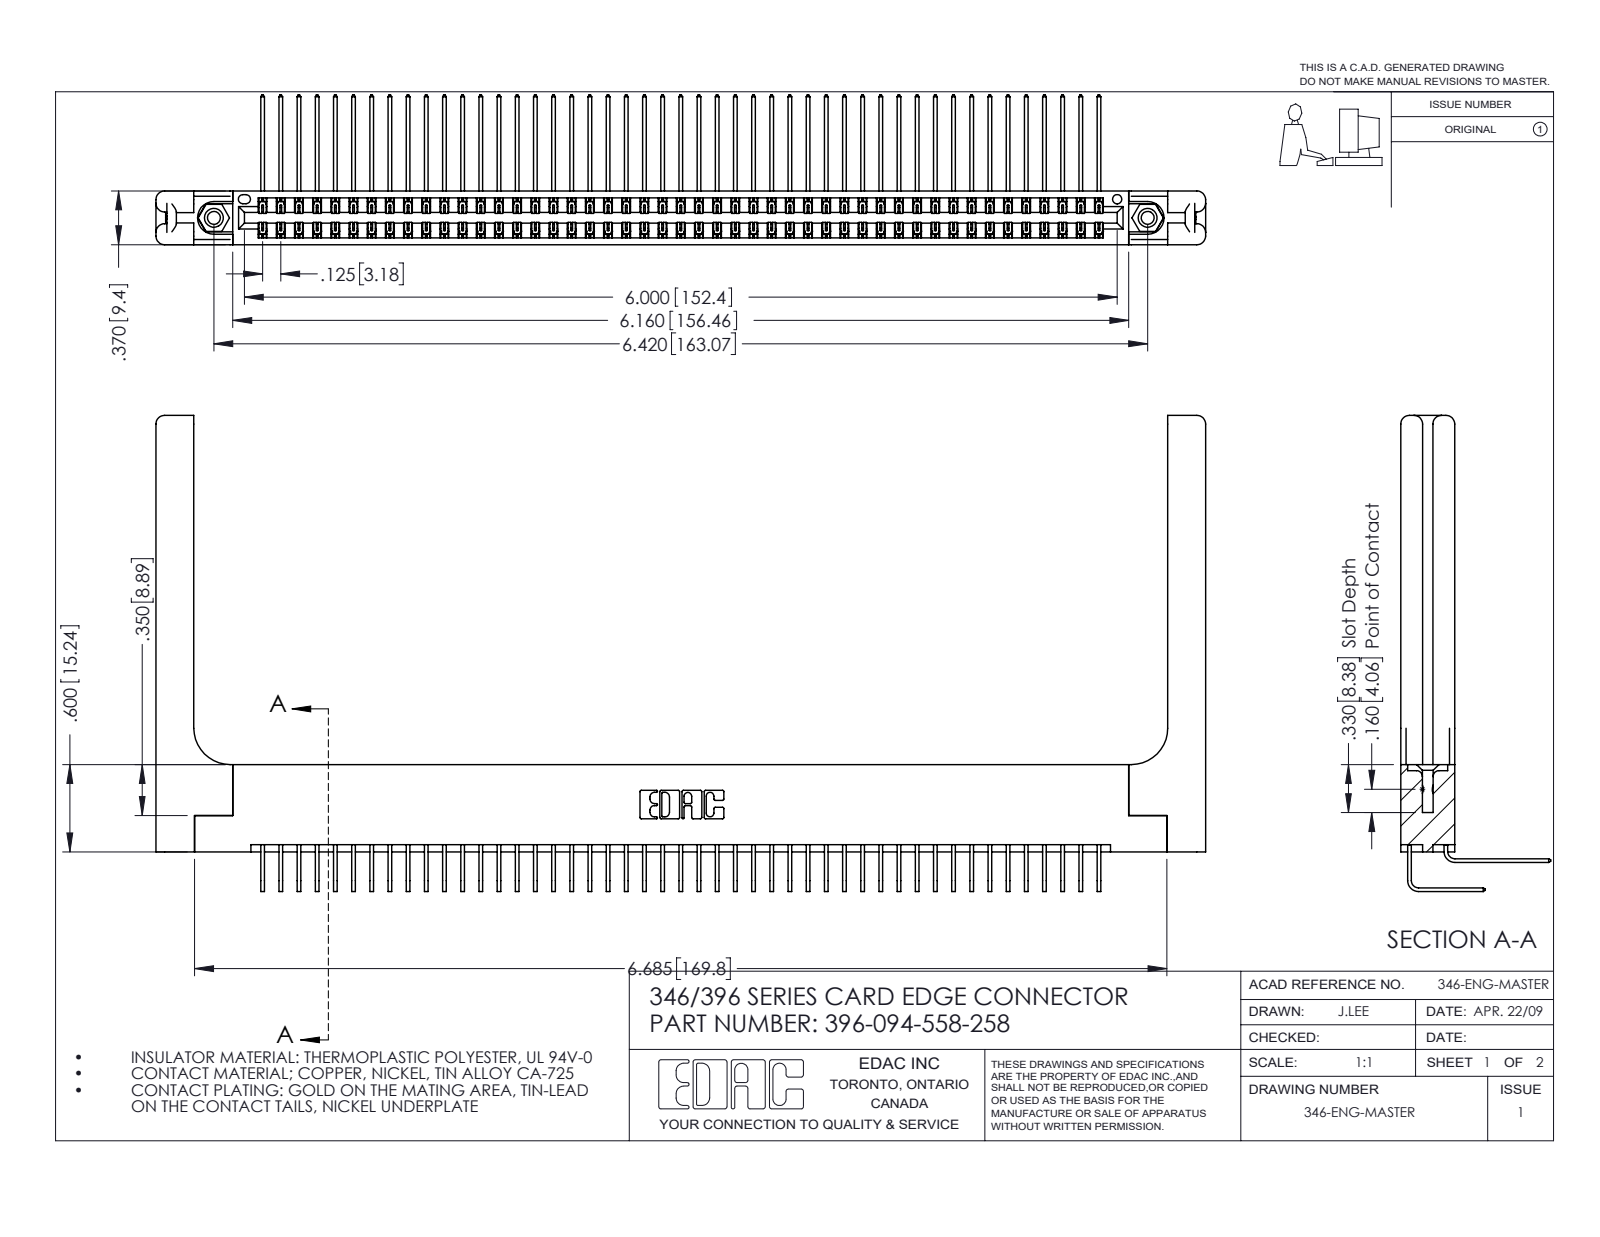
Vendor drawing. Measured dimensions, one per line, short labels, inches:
name: 345-250-001_345-250-001-102; 346-220-058_345-220-058; 345-292-001_558 559 Tail - 1; 346 Part_Flush Mounting Lugs - 0.156 Dia-TH (+2 more)
written by: SolidWorks 2016 (CONFIG_CONTROL_DESIGN)
unit: in
bodies: 99 solids, 5454 faces (3702 planar, 1692 cylindrical, 60 other)
size: 7.216 × 3.273 × 1.03
volume: 1.583 in³; area: 51.18 in²
holes: 2× ⌀0.089, 2× ⌀0.125, 2× ⌀0.156, 1× ⌀0.064
bosses: 2× ⌀0.155
rounds: 141× R0.006, 22× R0.01, 16× R0.06, 6× R0.007, 6× R0.031, 3× R0.026, 2× R0.014, 2× R0.022
face distances: 0.322, 0.048, 0.37, 0.072, 0.025, 0.298, 0.25, 0.148, 0.15, 0.275
hole spacings: 0.246, 6.211, 6.42
